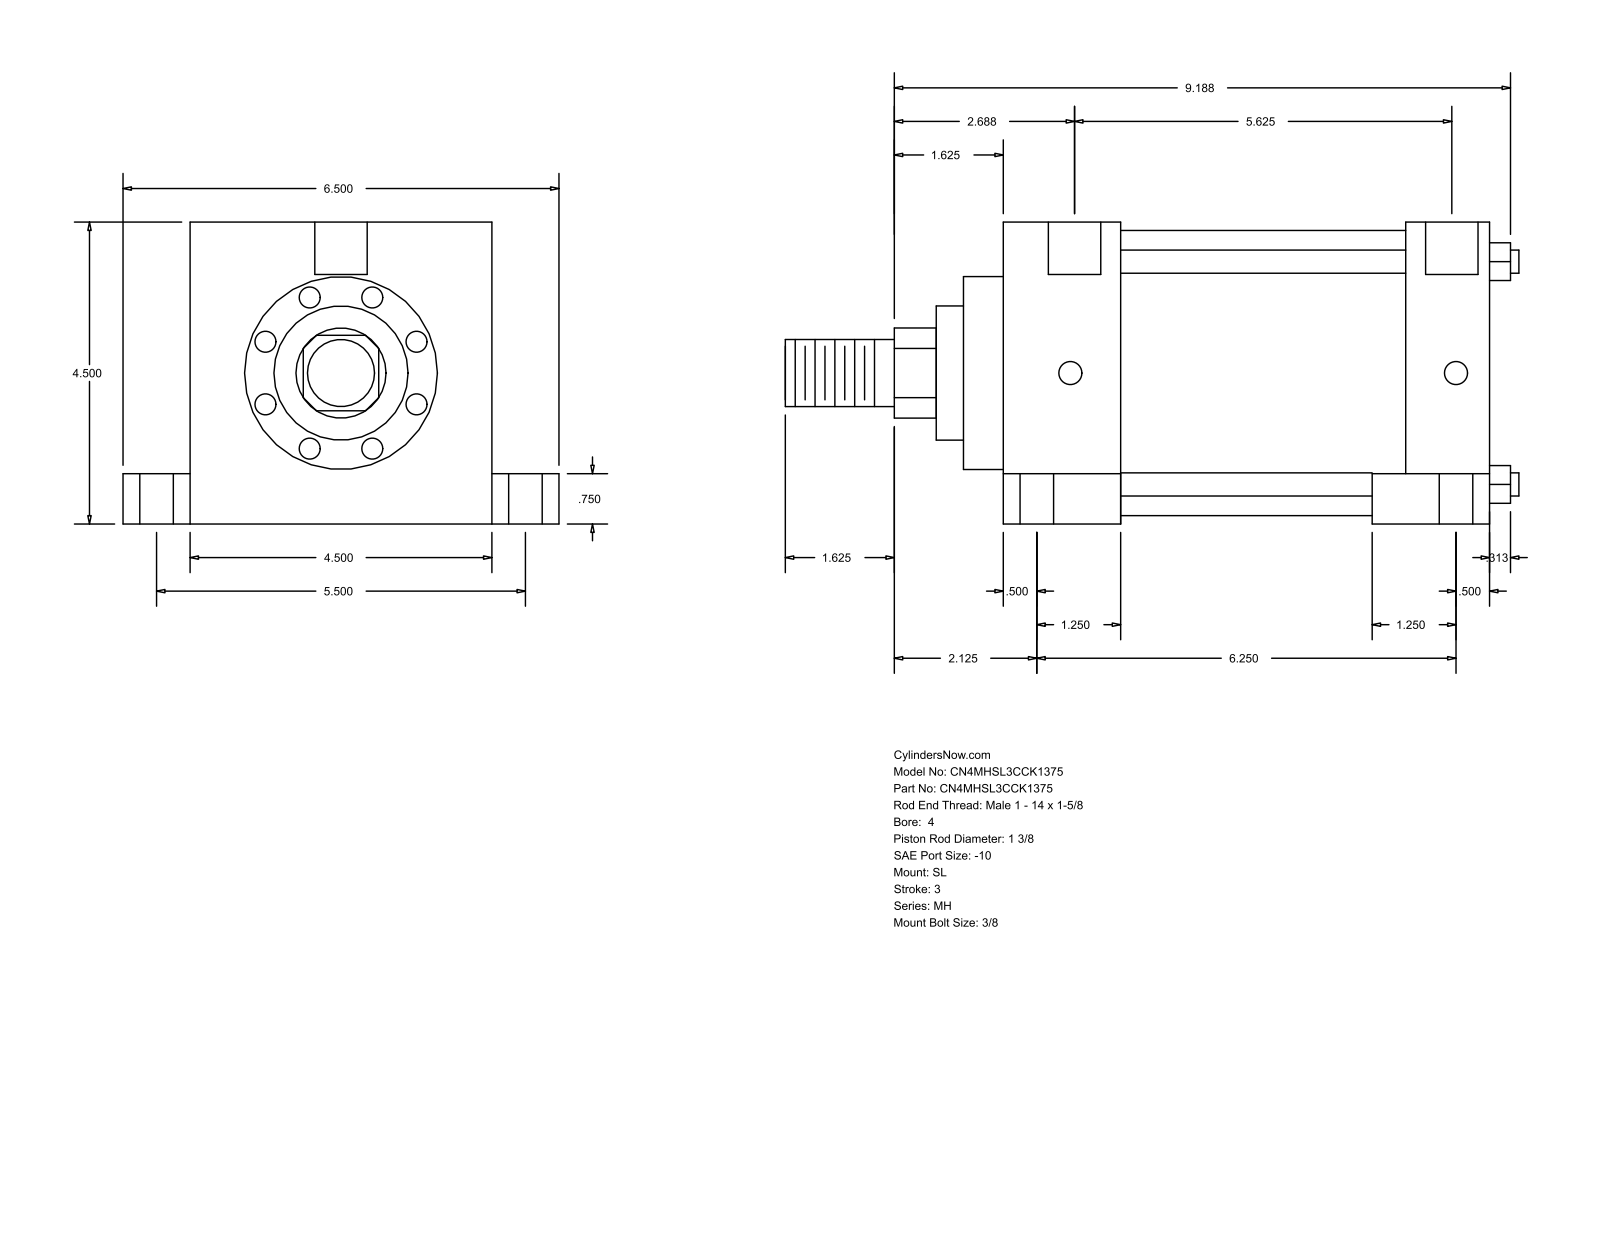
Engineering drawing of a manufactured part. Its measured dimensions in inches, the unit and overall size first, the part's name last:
Units: inches
Overall size (bounding box): 10.937 × 6.5 × 4.5
Round holes (diameter × count): ⌀0.344 ×4, ⌀0.5 ×4, ⌀0.75 ×4, ⌀0.781 ×2
Round bosses / shafts (diameter × count): ⌀0.345 ×4, ⌀4.25 ×1, ⌀2.875 ×1, ⌀2 ×1, ⌀1.375 ×1, ⌀1 ×1
Partial cylindrical surfaces — rounded edges, fillets, slot ends (radius × count): R0.672 ×1
Main face-to-face distances: 4.5, 7.25, 1.75, 5.5, 5.5, 3.75, 6, 4.25, 1.25, 1
Hole centre spacings: 2.75, 2.751, 2.795, 2.807, 5.5, 5.75, 6.25, 6.317
Bodies: 0 solids, 110 faces (77 planar, 33 cylindrical, 0 other)
Part name (STEP PRODUCT): MH_SL__0400_1.375
STEP written by: GSSL Pune (CONFIG_CONTROL_DESIGN)
